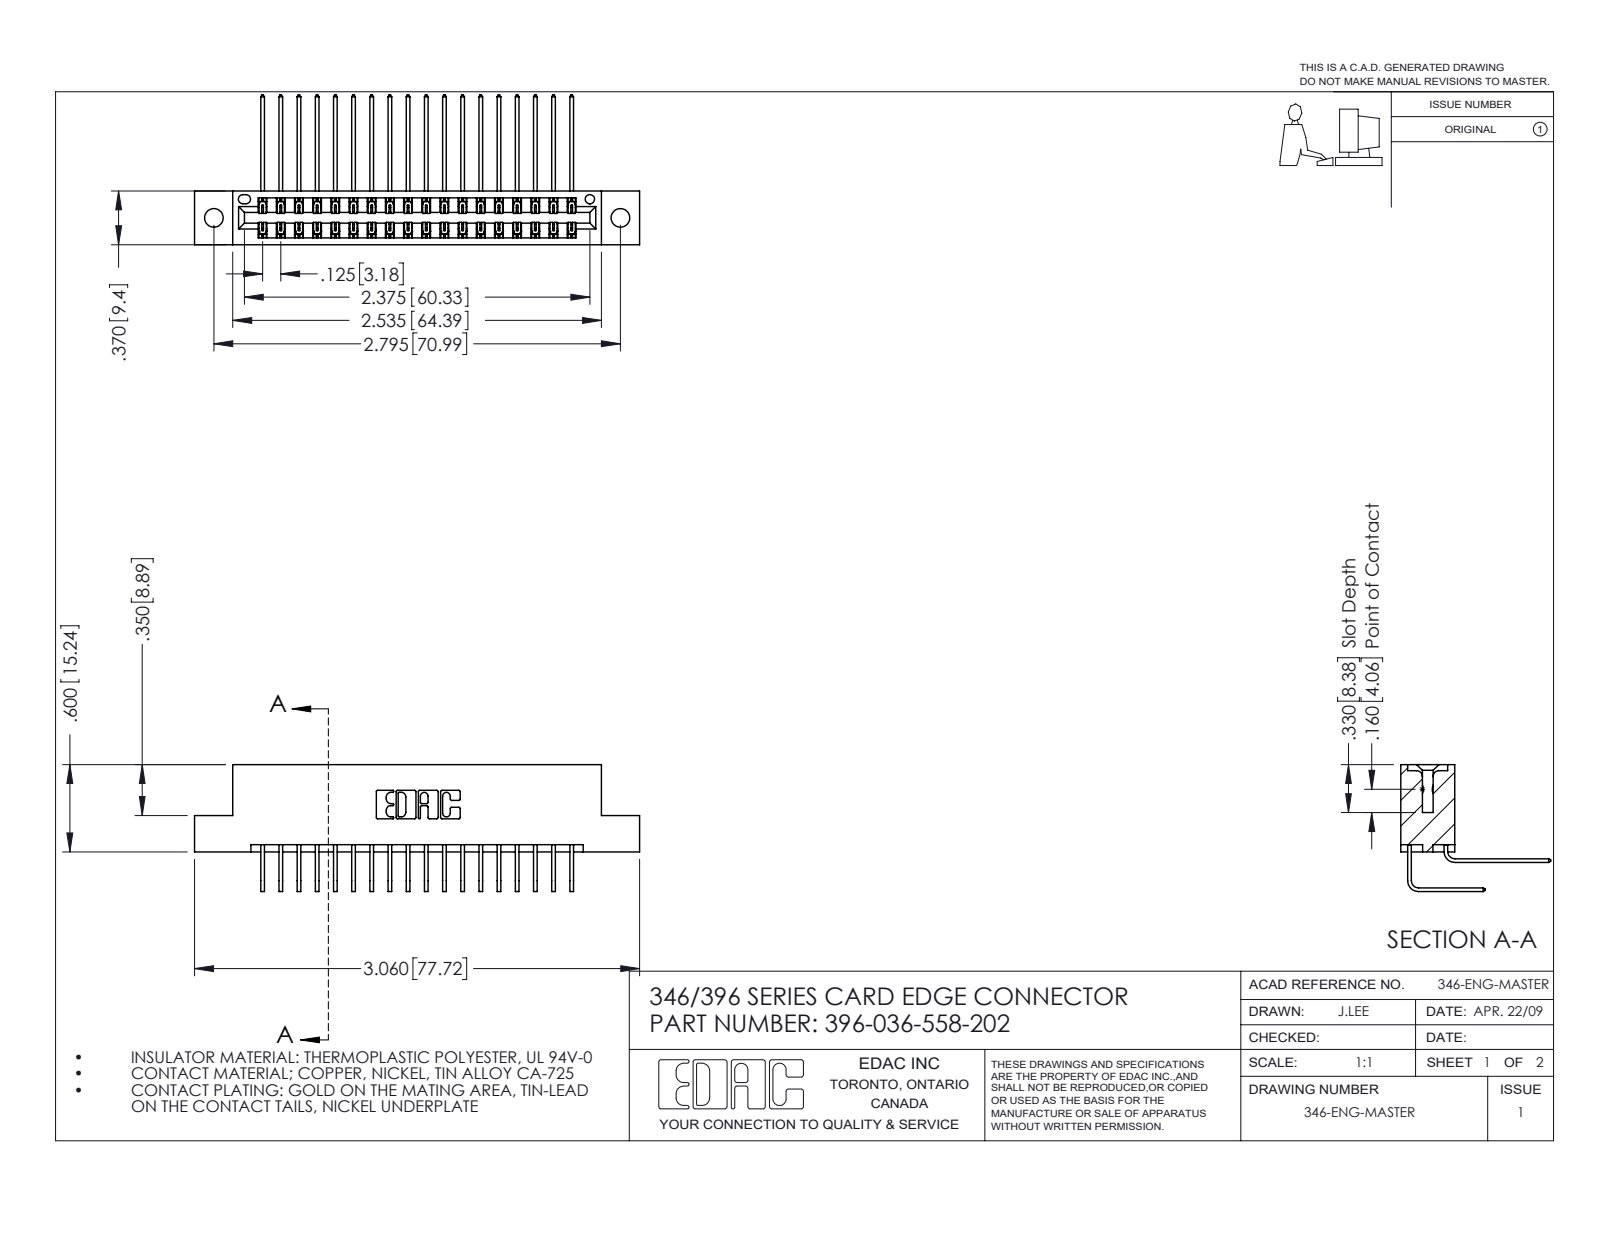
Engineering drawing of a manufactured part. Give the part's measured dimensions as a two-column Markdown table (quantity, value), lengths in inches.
| quantity | value |
| --- | --- |
| part name | 345-292-001_558 Tail - 2; 345-292-001_558 559 Tail - 1; 396-036-558-202; 346 Part_Flush Mounting Lugs - 0.128 Dia |
| STEP written by | SolidWorks 2016 (CONFIG_CONTROL_DESIGN) |
| units | inches |
| bodies | 37 solids, 2066 faces (1408 planar, 658 cylindrical, 0 other) |
| overall size | 3.06 × 1.03 × 0.873 |
| volume | 0.462 in³ |
| surface area | 16.66 in² |
| round holes (diameter × count) | 0.128 × 2, 0.064 × 1 |
| partial cylindrical surfaces (radius × count) | 0.006 × 54, 0.01 × 22, 0.007 × 6, 0.031 × 6, 0.026 × 3, 0.014 × 2, 0.022 × 2, 0.024 × 2 |
| main face-to-face distances | 0.322, 0.048, 0.25, 0.025, 0.37, 0.298, 0.072, 0.275, 0.148, 0.222 |
| hole center spacings | 0.246, 2.588, 2.795 |
